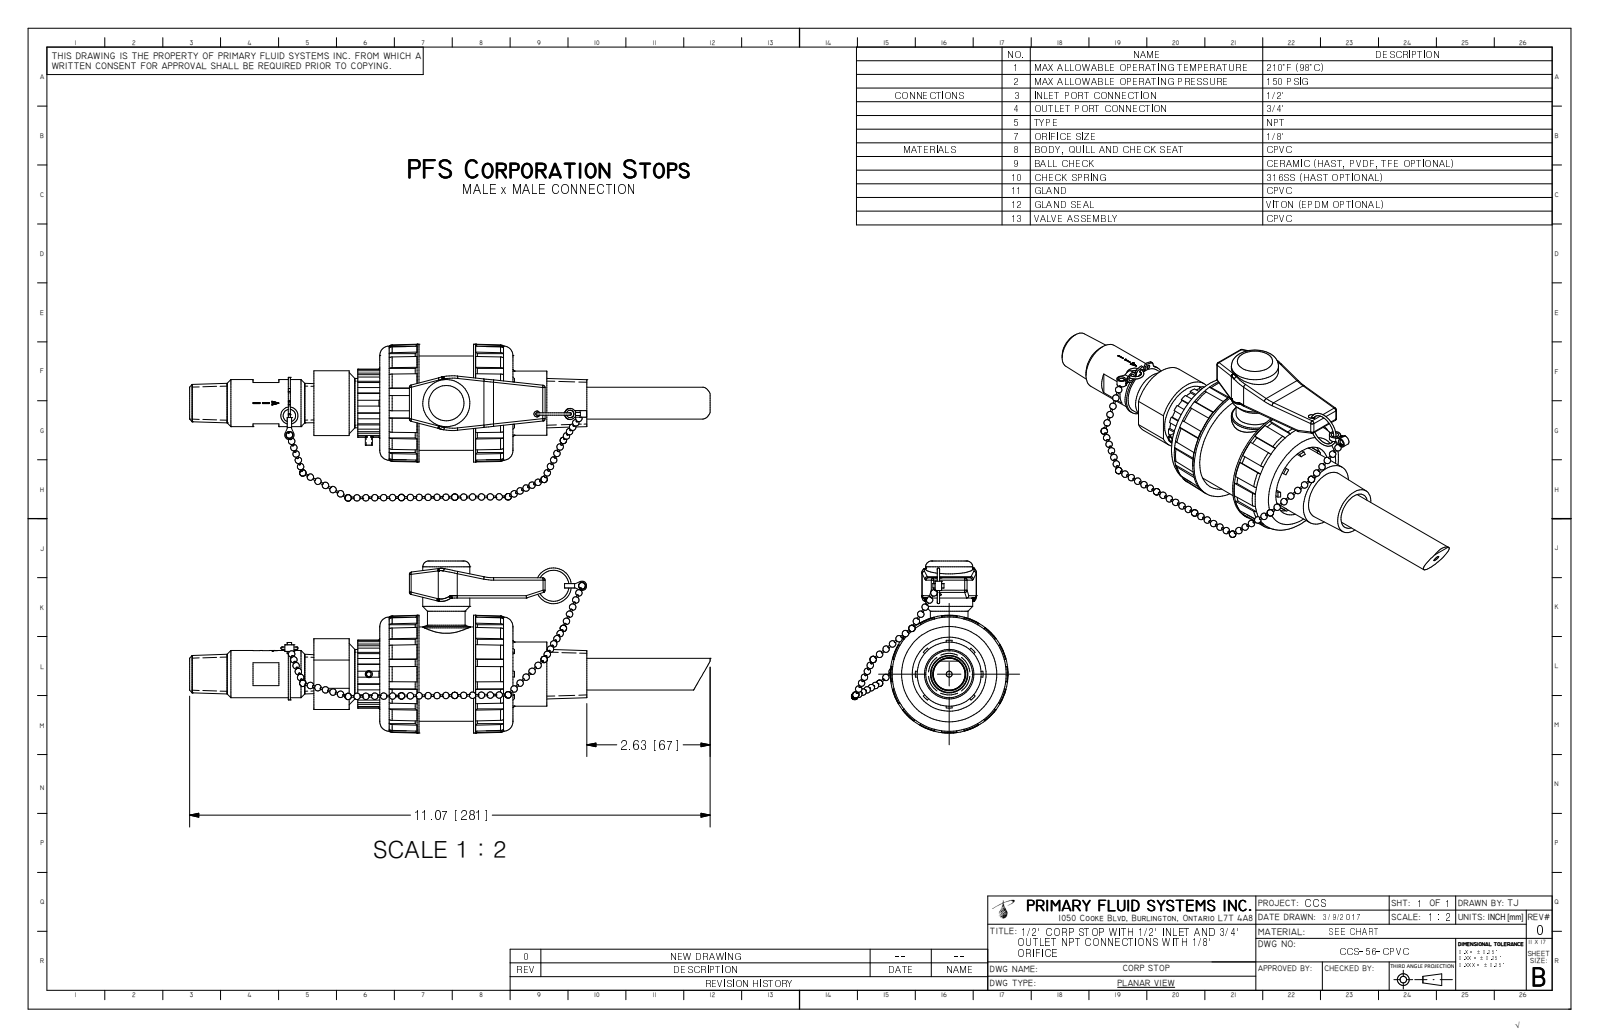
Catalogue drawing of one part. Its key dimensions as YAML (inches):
part_name: "CCS-56-CPVC_R0"
step_written_by: "Autodesk Inventor 2009 (AUTOMOTIVE_DESIGN)"
units: inches
bodies: {solids: 1, faces: 606, planar: 224, cylindrical: 147, other: 235}
overall_size: [11.069, 3.65, 3.328]
volume: 18.48
surface_area: 104.2
round_holes:
  - {diameter: 0.079, count: 1}
  - {diameter: 0.125, count: 1}
  - {diameter: 0.25, count: 1}
  - {diameter: 0.469, count: 1}
  - {diameter: 0.56, count: 1}
  - {diameter: 1.57, count: 1}
  - {diameter: 2.16, count: 1}
round_bosses_or_shafts:
  - {diameter: 1, count: 2}
  - {diameter: 2.5, count: 1}
  - {diameter: 2, count: 1}
  - {diameter: 1.801, count: 1}
  - {diameter: 1.36, count: 1}
  - {diameter: 1.094, count: 1}
  - {diameter: 0.8, count: 1}
  - {diameter: 0.675, count: 1}
partial_cylinders:
  - {radius: 0.05, count: 21}
  - {radius: 1, count: 3}
  - {radius: 0.043, count: 2}
  - {radius: 0.157, count: 2}
  - {radius: 0.351, count: 1}
  - {radius: 0.457, count: 1}
  - {radius: 0.463, count: 1}
  - {radius: 0.499, count: 1}
face_to_face_distances: [0.205, 2.625, 0.835, 1.995, 0.63, 1.79, 0.465, 2.83, 2.42, 1.16]
hole_center_spacings: [0.563]
